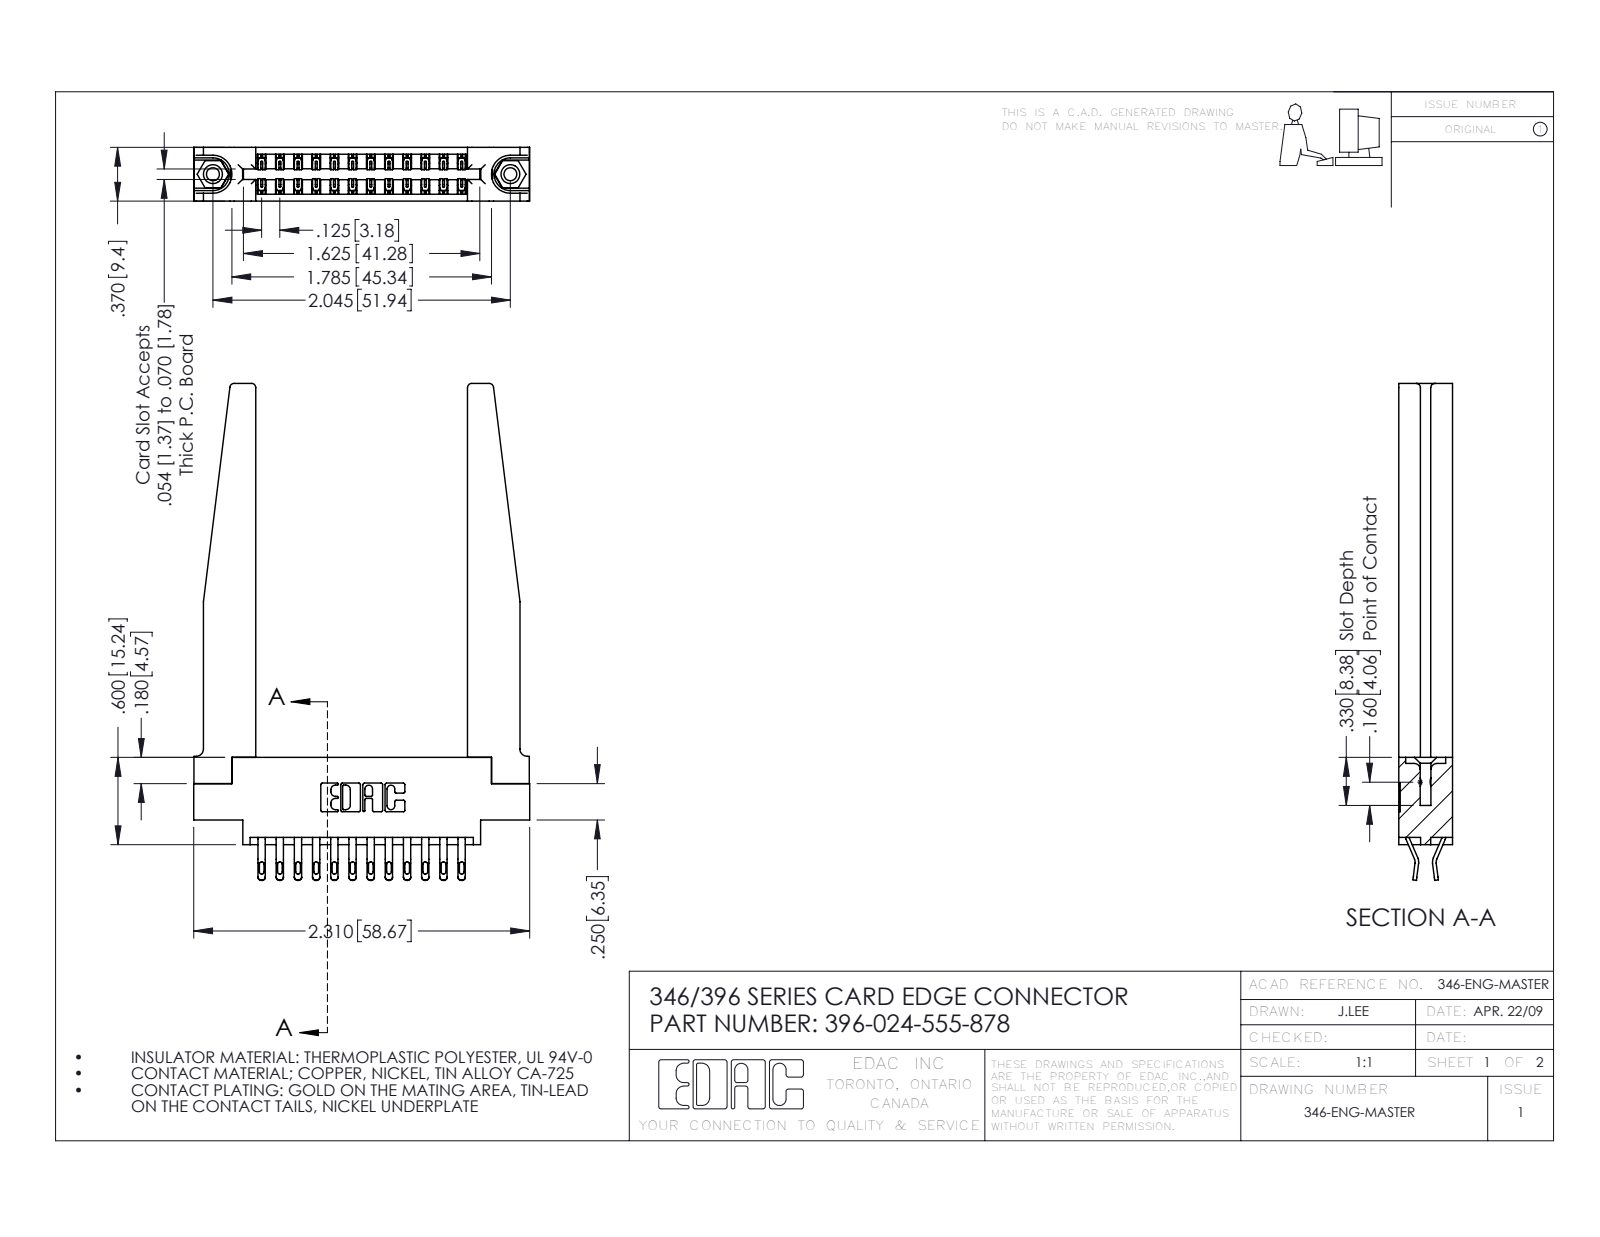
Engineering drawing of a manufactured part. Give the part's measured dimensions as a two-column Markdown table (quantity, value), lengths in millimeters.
| quantity | value |
| --- | --- |
| part name | 396-024-555-878; 346-220-078_345-220-078; 345-292-001_555 Tail; 345-250-001_345-250-001-102 (+1 more) |
| STEP written by | SolidWorks 2016 (CONFIG_CONTROL_DESIGN) |
| units | millimeters |
| bodies | 29 solids, 1752 faces (1014 planar, 686 cylindrical, 52 other) |
| overall size | 86.7 × 58.7 × 9.4 |
| volume | 12 300 mm³ |
| surface area | 13 920 mm² |
| round holes (diameter × count) | 2.3 × 2, 3.2 × 2, 4 × 2, 1.6 × 1 |
| round bosses / shafts (diameter × count) | 3.9 × 2 |
| partial cylindrical surfaces (radius × count) | 0.4 × 48, 0.5 × 48, 0.2 × 36, 0.3 × 22, 0.8 × 8, 0.2 × 6, 0.8 × 6, 1.3 × 4 |
| main face-to-face distances | 9.4, 3.8, 1.8, 3.8, 1.2, 8.2, 6.4, 2.6, 5.6, 4.4 |
| hole center spacings | 6.2, 46.7, 51.9 |
